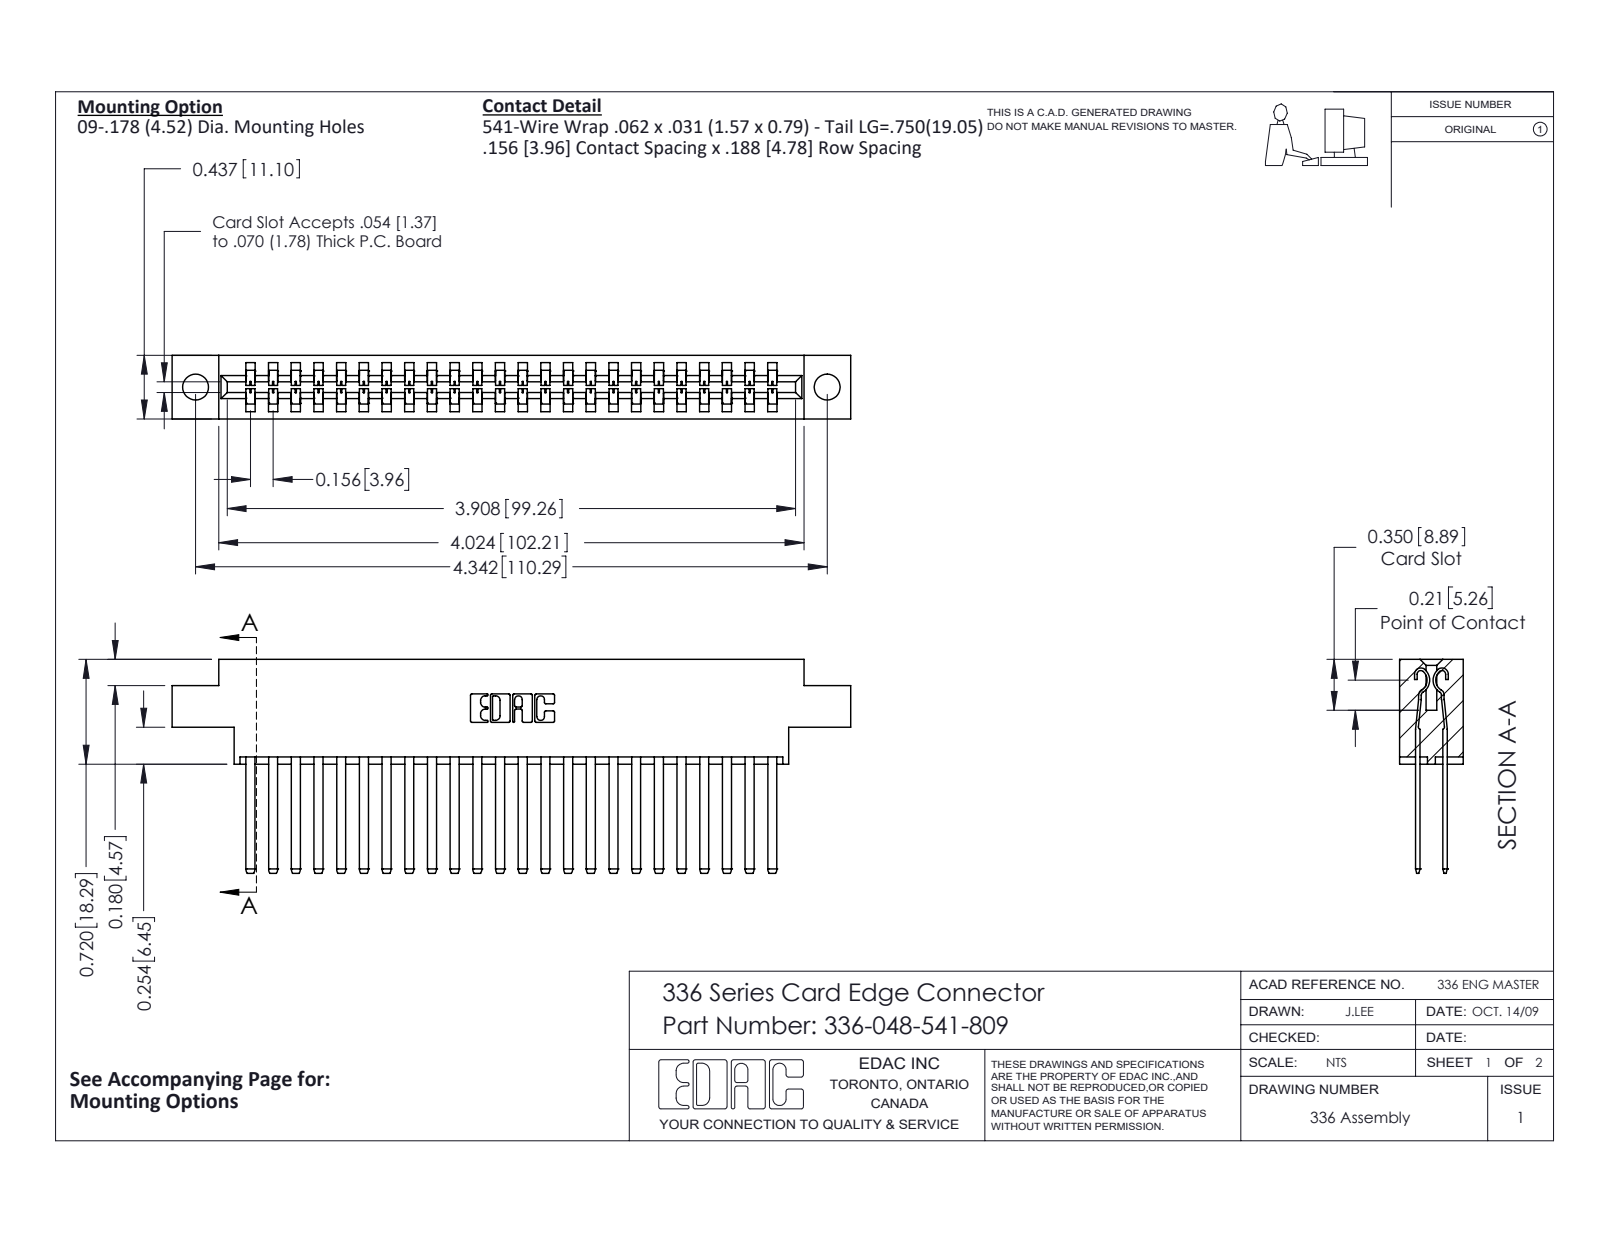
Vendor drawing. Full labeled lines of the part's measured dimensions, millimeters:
Part name (STEP PRODUCT): 336 Part_Offset - .178 Dia - TH; 336-290-001_336-290-541; 336-048-541-809
STEP written by: SolidWorks 2020 (CONFIG_CONTROL_DESIGN)
Units: millimetres
Bodies: 49 solids, 2134 faces (1322 planar, 812 cylindrical, 0 other)
Overall size (bounding box): 118.5 × 37.3 × 11.1
Volume: 17 570 mm³ · Surface area: 22 090 mm²
Round holes (diameter × count): ⌀4.5 ×2
Partial cylindrical surfaces — rounded edges, fillets, slot ends (radius × count): R0.1 ×96, R1.4 ×48, R0.3 ×22, R0.2 ×6, R0.8 ×6, R0.6 ×4, R1 ×4, R0.7 ×3
Main face-to-face distances: 4.8, 8.3, 3.6, 7.5, 2.8, 0.8, 11.1, 0.8, 4.6, 4
Hole centre spacings: 110.3
